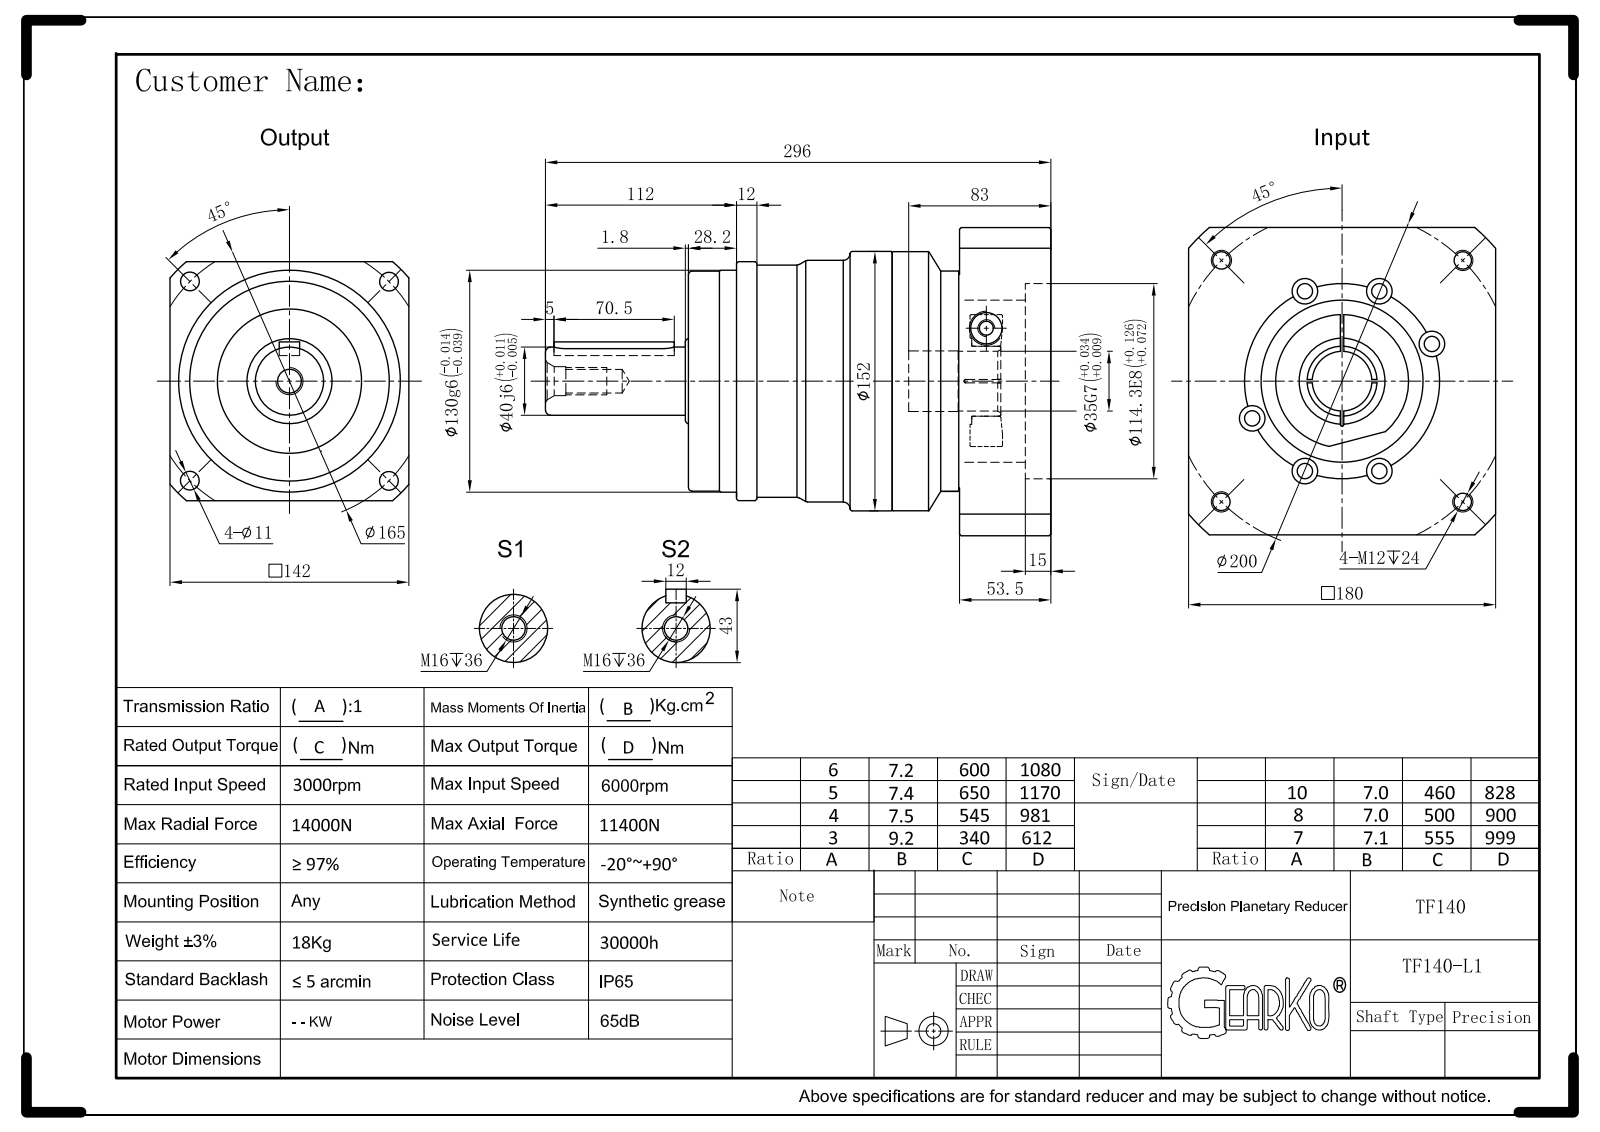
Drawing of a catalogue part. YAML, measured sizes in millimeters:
part_name: "TF140-L1-35-114.3-200-M12-83-15"
step_written_by: "SolidWorks 2017 (CONFIG_CONTROL_DESIGN)"
units: millimeters
bodies: {solids: 4, faces: 188, planar: 50, cylindrical: 80, other: 58}
overall_size: [296.3, 180, 180]
volume: 3947000
surface_area: 265794
round_holes:
  - {diameter: 10.2, count: 4}
  - {diameter: 11, count: 4}
  - {diameter: 17, count: 2}
  - {diameter: 16, count: 1}
  - {diameter: 17.5, count: 1}
  - {diameter: 35, count: 1}
  - {diameter: 41, count: 1}
  - {diameter: 50, count: 1}
  - {diameter: 50.5, count: 1}
  - {diameter: 95, count: 1}
  - {diameter: 114.3, count: 1}
  - {diameter: 125, count: 1}
round_bosses_or_shafts:
  - {diameter: 152, count: 1}
  - {diameter: 151.8, count: 1}
  - {diameter: 141.5, count: 1}
  - {diameter: 136, count: 1}
  - {diameter: 130, count: 1}
  - {diameter: 129, count: 1}
  - {diameter: 128.8, count: 1}
  - {diameter: 78, count: 1}
partial_cylinders:
  - {radius: 0.5, count: 4}
  - {radius: 6, count: 3}
  - {radius: 1, count: 1}
  - {radius: 92.5, count: 1}
  - {radius: 119, count: 1}
face_to_face_distances: [53.5, 180, 3, 50.5, 159, 162, 212.5, 19, 28.2, 130.8]
hole_center_spacings: [129.64, 100, 141.42, 182.5, 17.49, 17.5, 82.5, 82.51]
